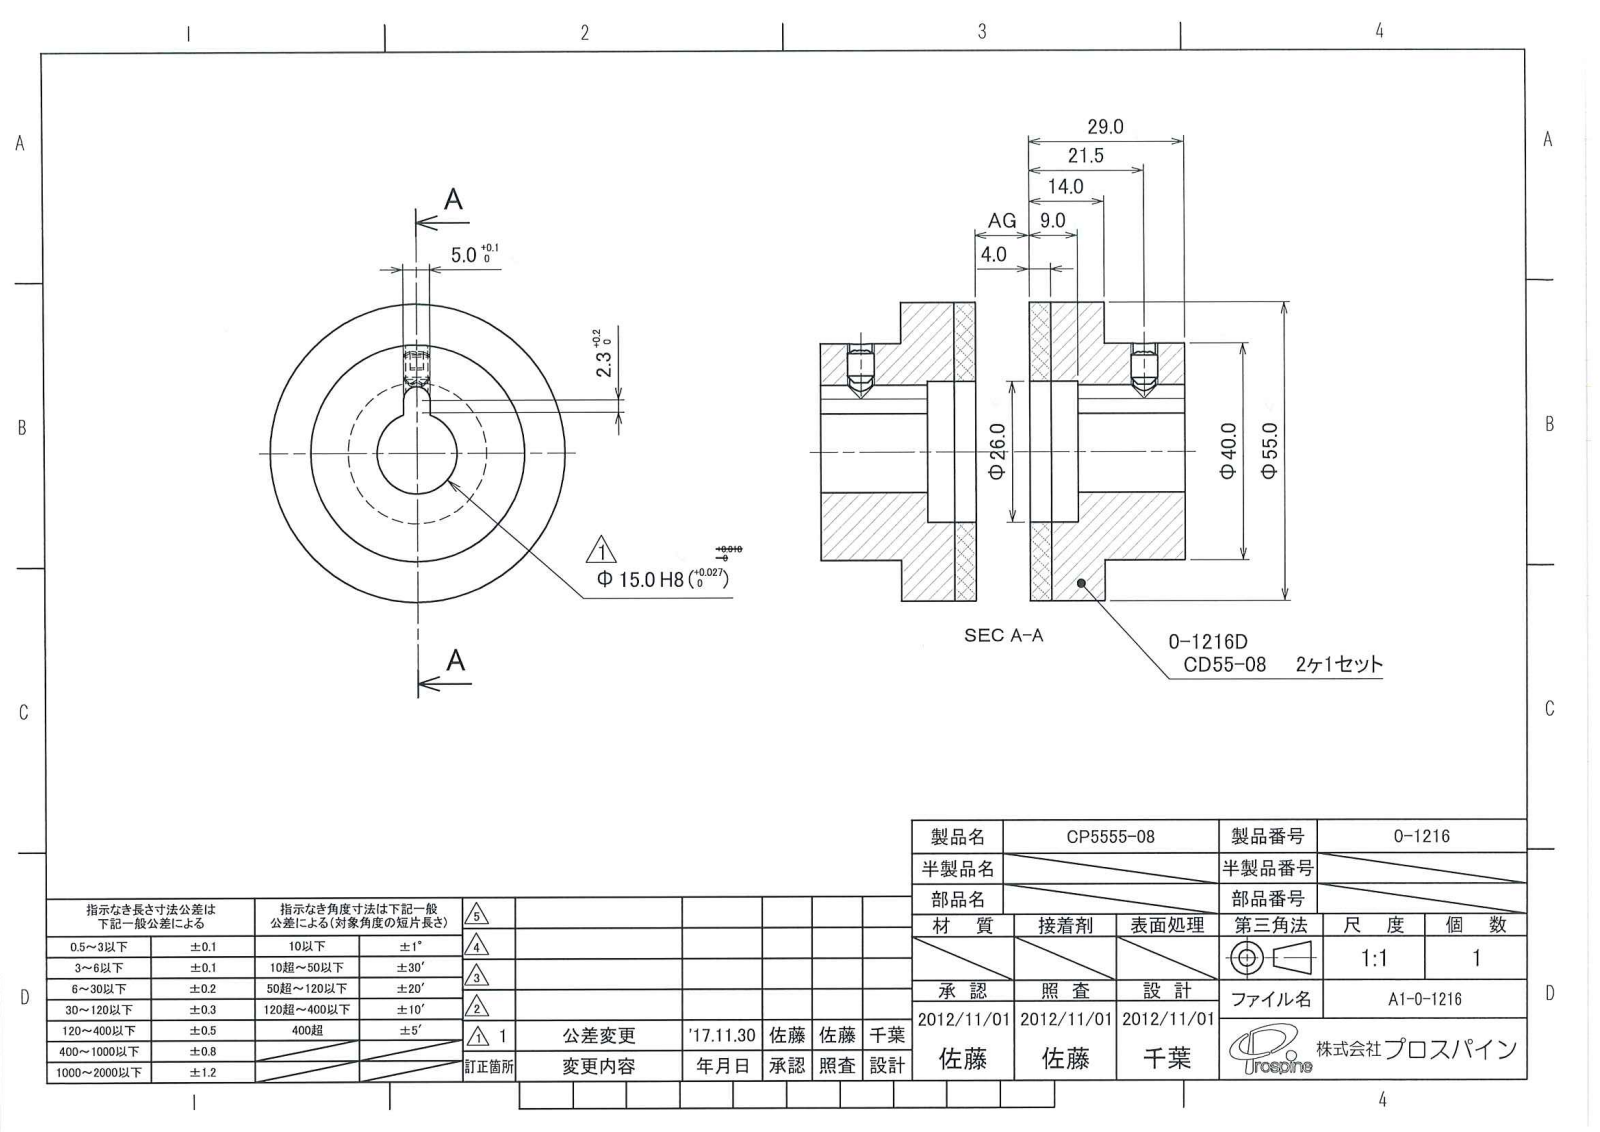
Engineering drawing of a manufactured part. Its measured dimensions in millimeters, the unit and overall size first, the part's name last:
Units: millimetres
Overall size (bounding box): 55 × 55 × 29
Round holes (diameter × count): ⌀4.2 ×1, ⌀15 ×1, ⌀26 ×1
Round bosses / shafts (diameter × count): ⌀55 ×1, ⌀40 ×1, ⌀5 ×1
Partial cylindrical surfaces — rounded edges, fillets, slot ends (radius × count): R2.5 ×1
Main face-to-face distances: 4, 14, 10, 29, 25, 15, 5, 9, 20, 2.5
Volume: 43 418 mm³ · Surface area: 14 545 mm²
Bodies: 4 solids, 38 faces (22 planar, 10 cylindrical, 6 other)
STEP written by: PSStep 10.0 (CONFIG_CONTROL_DESIGN)
